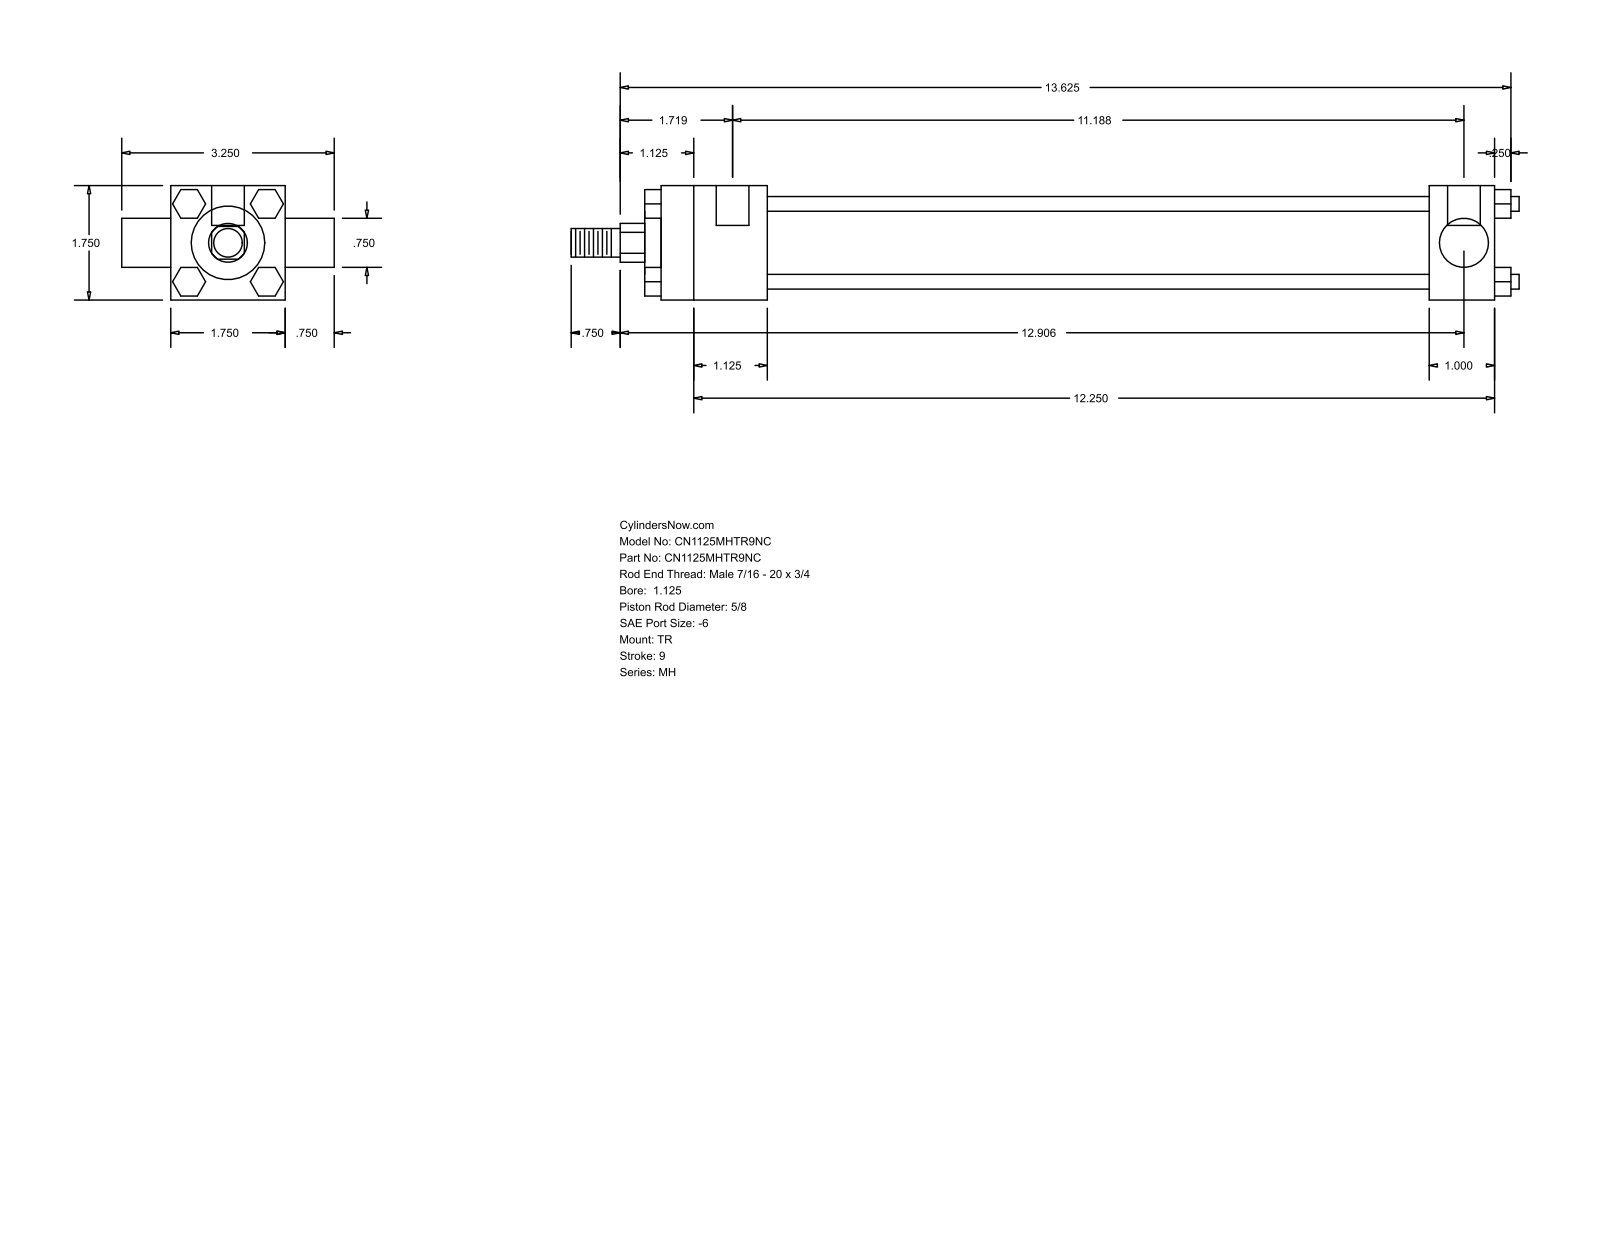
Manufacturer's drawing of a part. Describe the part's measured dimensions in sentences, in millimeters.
The part is named "MH_TR__0112_0.625". Its 3-D file was written by "GSSL Pune (CONFIG_CONTROL_DESIGN)". It is 0 solids with 120 faces: 92 planar, 28 cylindrical and 0 other. Overall it measures 368.3 by 82.55 by 44.45 millimeters. Round holes: 3 of diameter 5.56, 2 of diameter 12.7. Round bosses or shafts: 4 of diameter 5.71, 1 of diameter 34.92, 1 of diameter 28.57, 1 of diameter 19.05, 1 of diameter 15.88, 1 of diameter 11.11. Partial cylindrical surfaces (rounded edges, fillets, slot ends): 1 of radius 7.54. The main face-to-face distances are 44.46, 11.11, 257.17, 282.58, 25.41, 41.27, 298.44, 323.85, 47.62, 6.35. The hole center spacings are 3.17, 280.99, 284.16.
